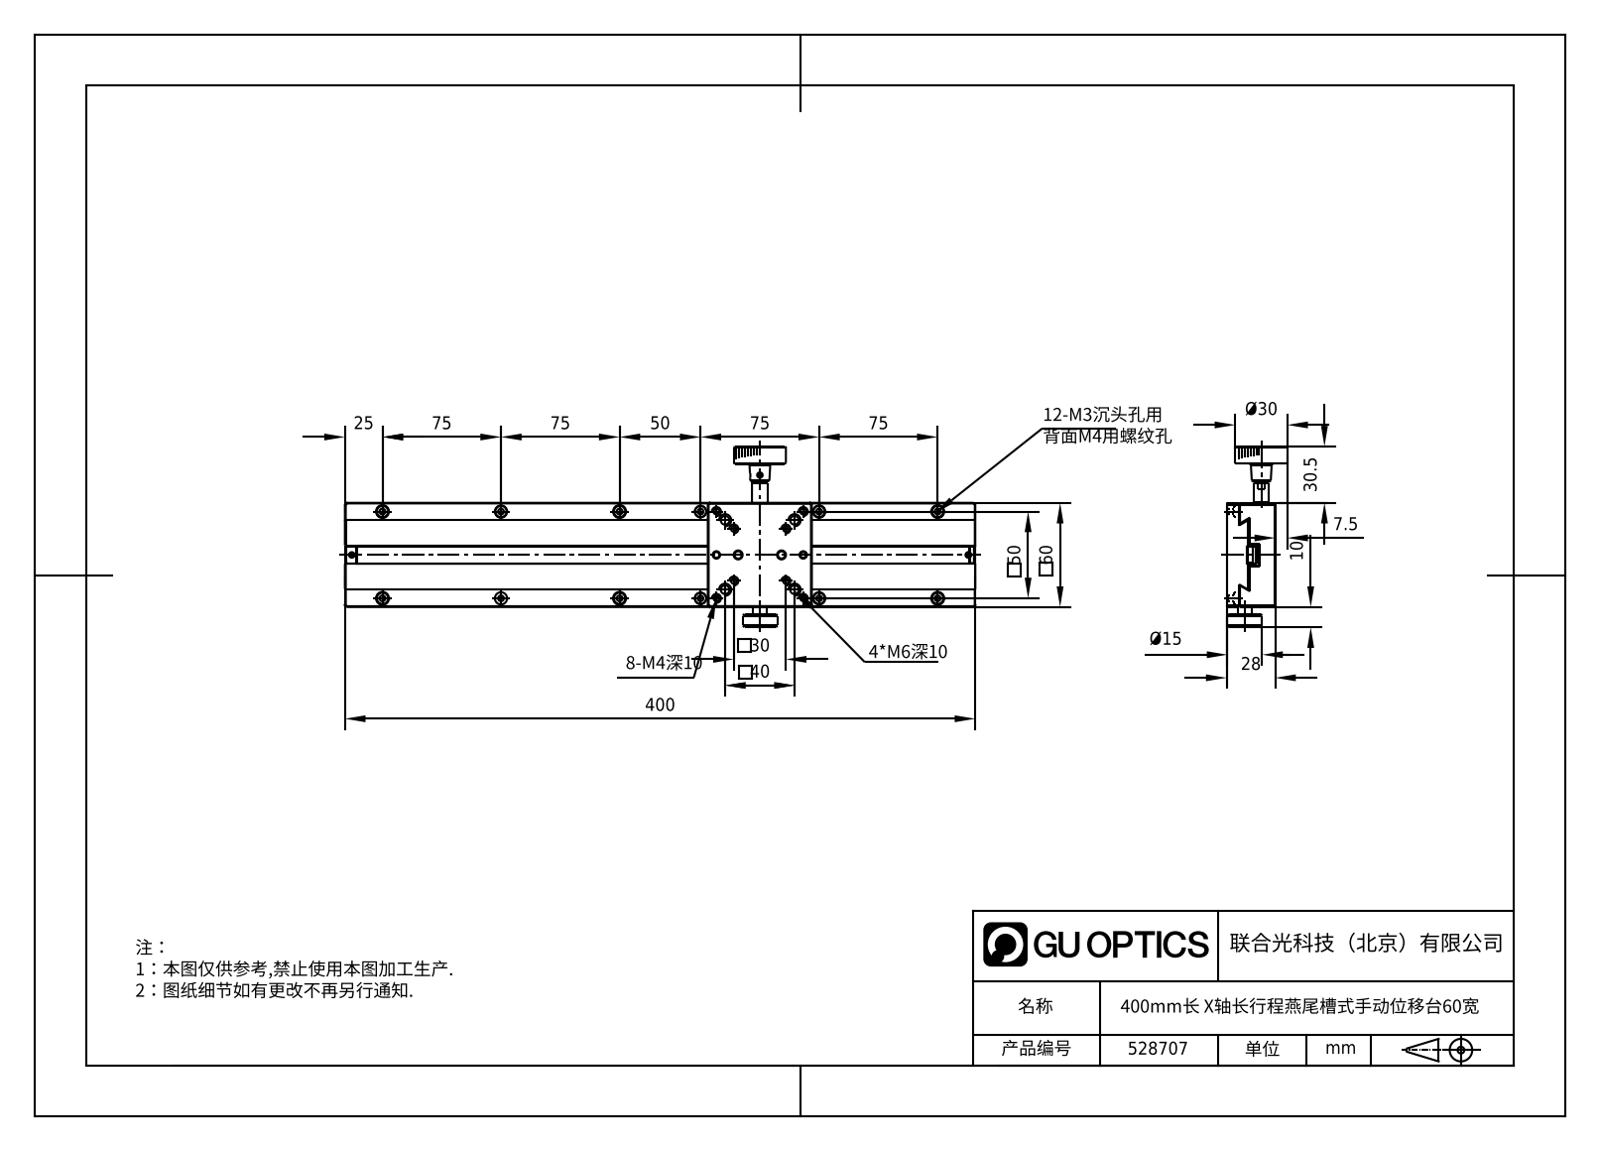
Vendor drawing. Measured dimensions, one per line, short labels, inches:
name: 528707
written by: SolidWorks 2020 (CONFIG_CONTROL_DESIGN)
unit: in
bodies: 19 solids, 667 faces (302 planar, 166 cylindrical, 199 other)
size: 15.748 × 4.007 × 1.3
volume: 19.14 in³; area: 153.6 in²
holes: 19× ⌀0.13, 12× ⌀0.236, 10× ⌀0.098, 9× ⌀0.197, 6× ⌀0.081, 6× ⌀0.114, 1× ⌀0.157, 1× ⌀0.161, 1× ⌀0.177, 1× ⌀0.315, 1× ⌀0.394
bosses: 5× ⌀0.118, 4× ⌀0.177, 4× ⌀0.098, 2× ⌀0.354, 2× ⌀0.157, 1× ⌀1.181, 1× ⌀0.394, 1× ⌀0.315
rounds: 1× R0.041
face distances: 0.295, 0.48, 0.185, 0.39, 0.094, 0.091, 2.362, 1.024, 1.102, 1.339
hole spacings: 2.65, 5.502, 2.953, 0.278, 1.1, 1.392, 1.623, 1.783
